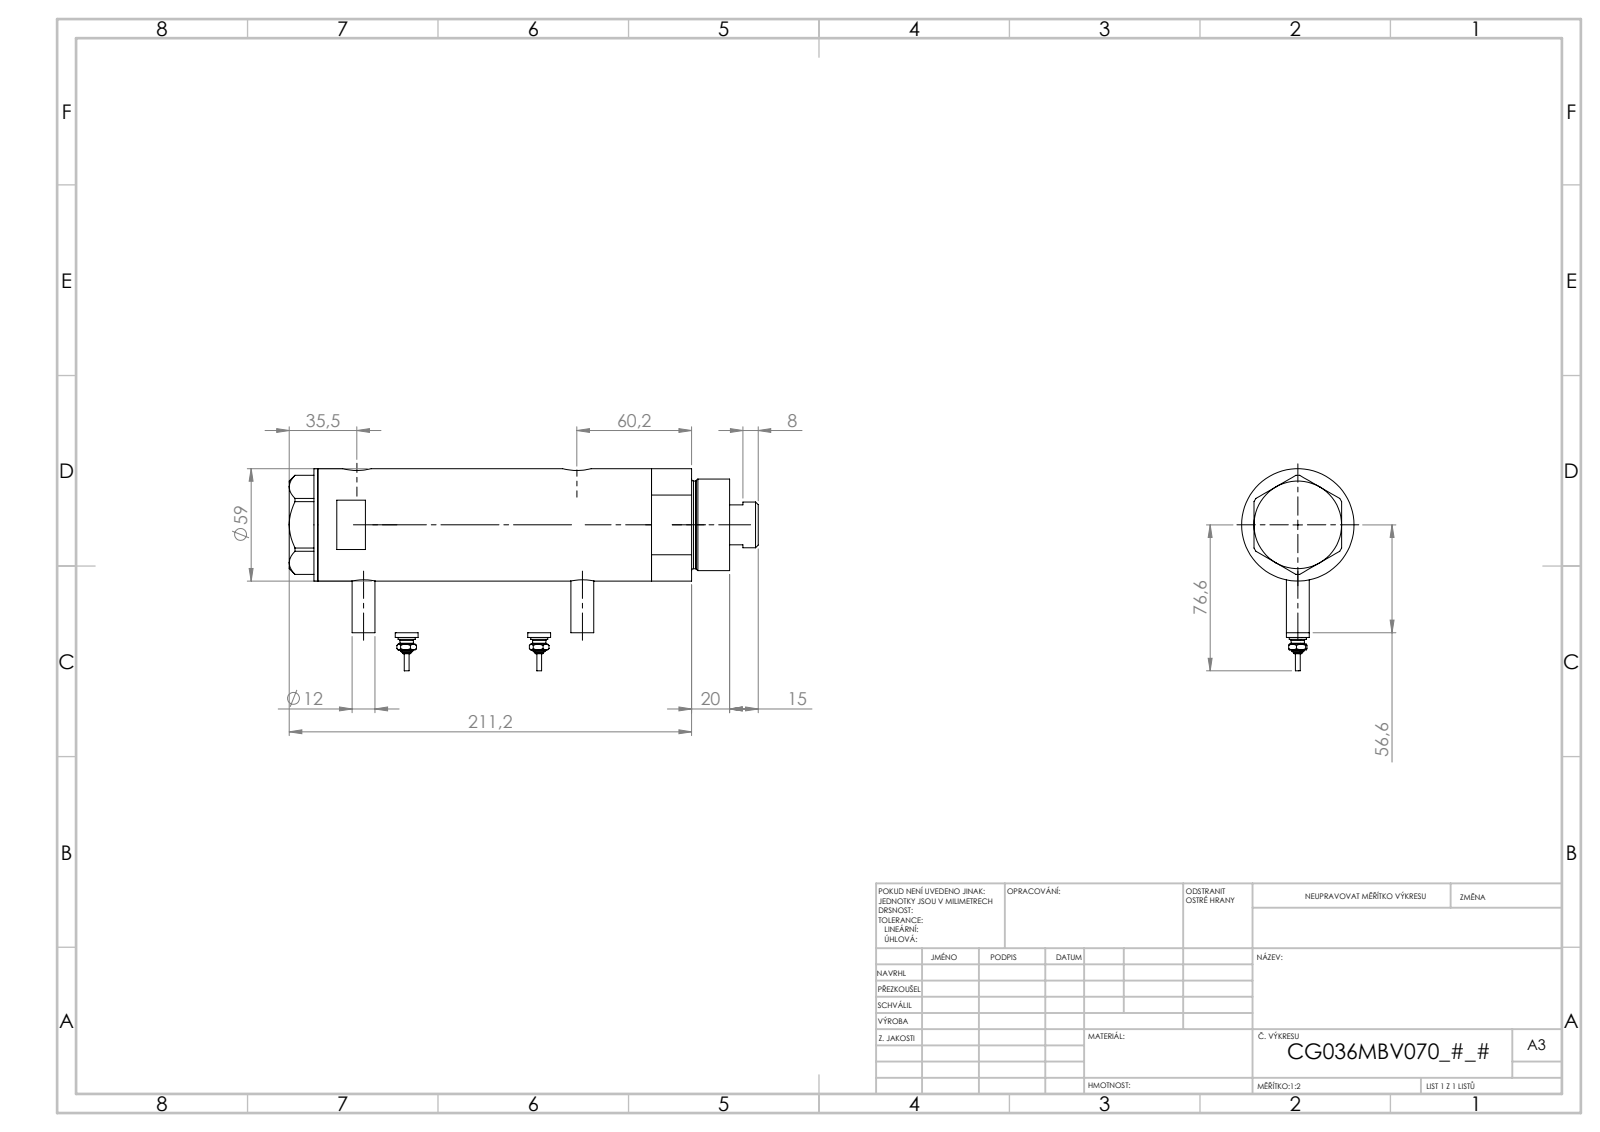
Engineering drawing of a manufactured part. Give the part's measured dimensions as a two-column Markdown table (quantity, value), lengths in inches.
| quantity | value |
| --- | --- |
| part name | V270CG_VC; V270CG_SWITCH; V270CG_MIDDLE; V270CG_BACK (+1 more) |
| STEP written by | SolidWorks 2019 (CONFIG_CONTROL_DESIGN) |
| units | inches |
| bodies | 6 solids, 232 faces (81 planar, 77 cylindrical, 74 other) |
| overall size | 9.19 × 3.594 × 2.323 |
| volume | 32.25 in³ |
| surface area | 170.9 in² |
| round holes (diameter × count) | 0.197 × 2, 0.383 × 2, 0.492 × 2, 0.591 × 2, 0.335 × 1, 0.984 × 1, 1.043 × 1, 1.417 × 1, 1.575 × 1, 2.047 × 1 |
| round bosses / shafts (diameter × count) | 0.472 × 4, 0.354 × 2, 0.276 × 2, 0.171 × 2, 0.094 × 2, 2.323 × 1, 1.89 × 1, 1.811 × 1 |
| main face-to-face distances | 5.013, 0.925, 4.088, 0.591, 1.516, 5.604, 8.599, 8.009, 7.083, 2.995 |
| hole center spacings | 0.114, 0.138, 4.022, 4.136, 4.159, 4.274, 0.114, 0.115 |
